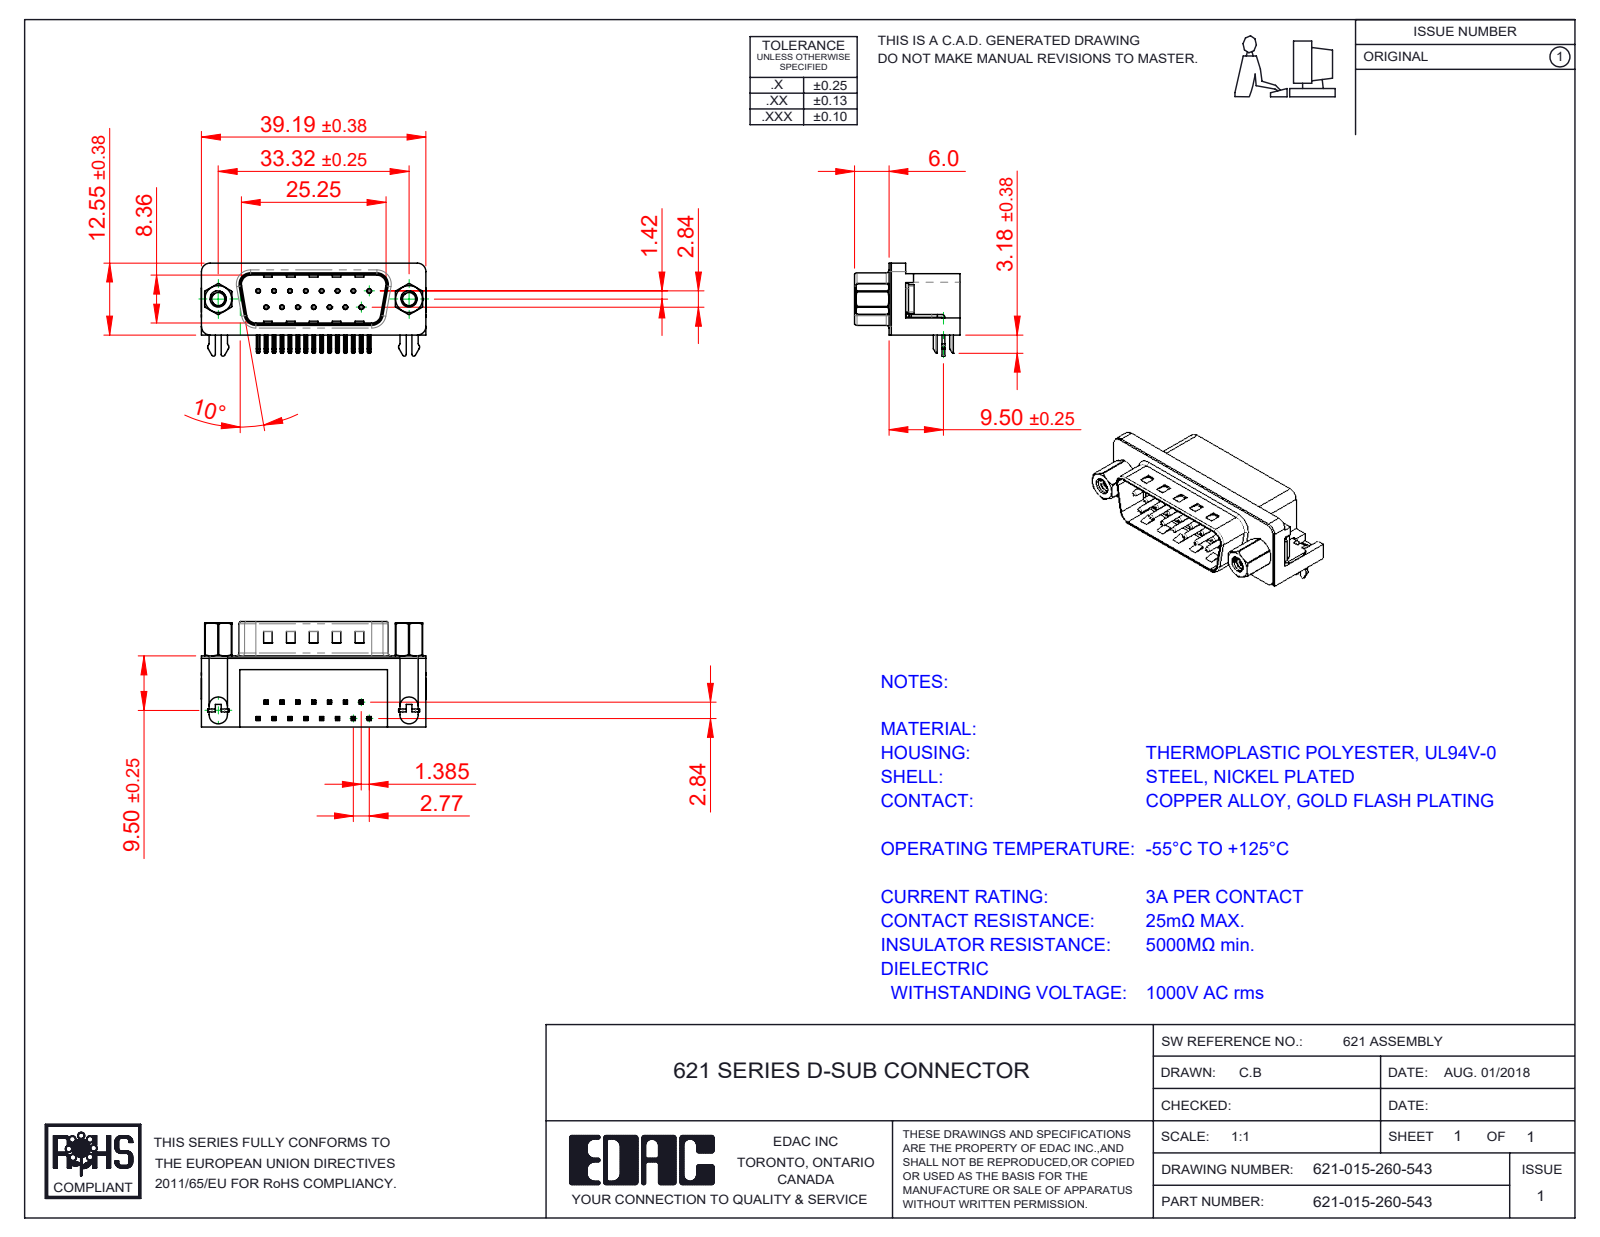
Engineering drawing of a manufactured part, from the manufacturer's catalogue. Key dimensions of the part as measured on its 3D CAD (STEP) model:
Part name (STEP PRODUCT): 621 Housing_15 Socket; 621 4 Prong Board Lock; 621-015-260-543; 621 4-40 Threaded Rivet (+4 more)
STEP written by: SolidWorks 2016 (CONFIG_CONTROL_DESIGN)
Units: millimetres
Bodies: 23 solids, 1723 faces (957 planar, 523 cylindrical, 243 other)
Overall size (bounding box): 39.22 × 18.4 × 16.25
Volume: 4 638 mm³ · Surface area: 6 208 mm²
Round holes (diameter × count): ⌀0.35 ×15, ⌀0.8 ×15, ⌀2 ×2, ⌀2.26 ×2, ⌀2.29 ×2, ⌀4 ×2, ⌀4.8 ×2, ⌀5 ×2
Round bosses / shafts (diameter × count): ⌀0.75 ×15, ⌀4.9 ×2, ⌀4.75 ×2, ⌀3.9 ×2, ⌀3 ×2, ⌀2.79 ×2
Partial cylindrical surfaces — rounded edges, fillets, slot ends (radius × count): R0.25 ×72, R0.12 ×30, R1 ×16, R0.5 ×9, R1.6 ×8, R1.5 ×6, R0.9 ×4, R2 ×4
Main face-to-face distances: 0.4, 12, 10.35, 12.4, 2.1, 10.46, 1.7, 10.86, 8.76, 9.5
Hole centre spacings: 3.16, 2.77, 5.54, 8.31, 11.08, 5.03, 5.04, 7.48
